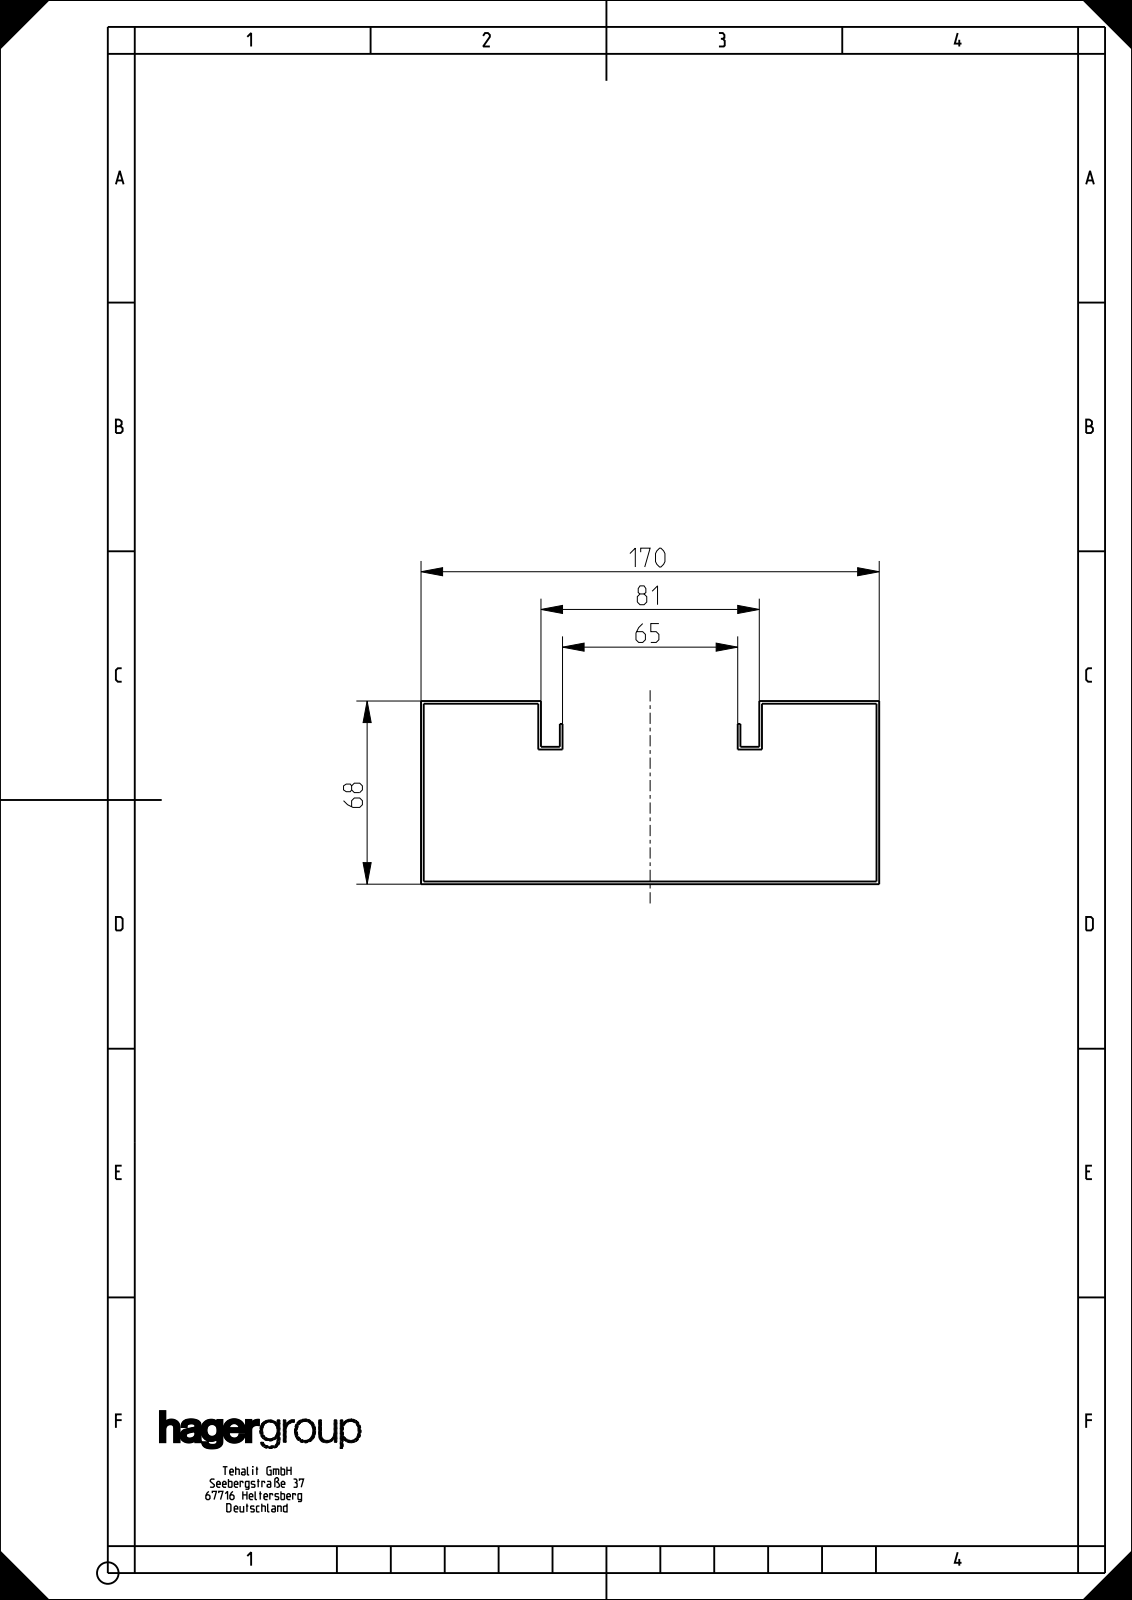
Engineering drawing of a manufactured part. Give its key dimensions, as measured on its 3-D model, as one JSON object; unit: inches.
{"part_name": "BRS651701KUN", "step_written_by": "CREO PARAMETRIC BY PTC INC, 2022162 (AUTOMOTIVE_DESIGN)", "units": "inches", "bodies": {"solids": 1, "faces": 858, "planar": 826, "cylindrical": 32, "other": 0}, "overall_size": [78.74, 6.693, 2.677], "volume_in3": 55.67, "surface_area_in2": 2840, "round_holes": [[0.256, 16]], "face_to_face_distances": [0.039, 2.638, 6.654, 2.598, 2.677, 1.713, 4.941, 6.693, 6.614, 2.028], "hole_center_spacings": [9.843, 10.221, 19.685, 19.877, 29.528, 29.656, 2.756, 39.37]}
